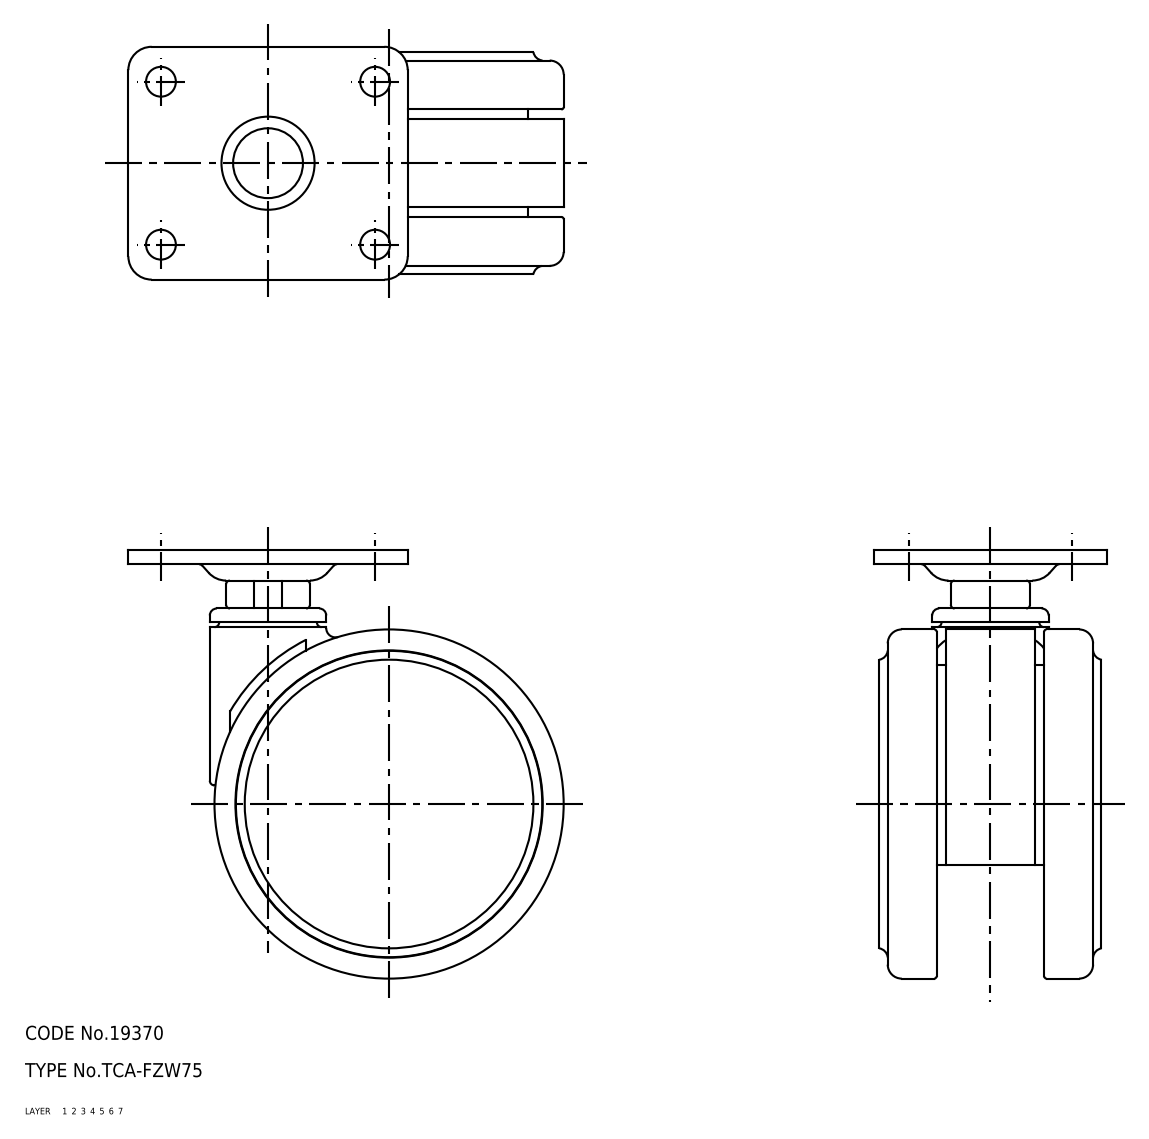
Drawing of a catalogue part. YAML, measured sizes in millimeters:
part_name: "caster; TCA-FZW75"
step_written_by: "SolidWorks 2015 (AUTOMOTIVE_DESIGN)"
units: millimeters
bodies: {solids: 2, faces: 1831, planar: 428, cylindrical: 783, other: 620}
overall_size: [93.5, 92, 50]
volume: 120349
surface_area: 74778
round_holes:
  - {diameter: 6.4, count: 4}
  - {diameter: 6.5, count: 1}
  - {diameter: 8, count: 1}
  - {diameter: 8.1, count: 1}
  - {diameter: 10.2, count: 1}
  - {diameter: 11, count: 1}
  - {diameter: 17, count: 1}
  - {diameter: 18.1, count: 1}
  - {diameter: 19, count: 1}
  - {diameter: 22.6, count: 1}
  - {diameter: 59, count: 1}
  - {diameter: 63, count: 1}
round_bosses_or_shafts:
  - {diameter: 16, count: 2}
  - {diameter: 14, count: 2}
  - {diameter: 65.8, count: 1}
  - {diameter: 54, count: 1}
  - {diameter: 26, count: 1}
  - {diameter: 25, count: 1}
  - {diameter: 10, count: 1}
  - {diameter: 8, count: 1}
partial_cylinders:
  - {radius: 1, count: 139}
  - {radius: 0.3, count: 132}
  - {radius: 0.5, count: 127}
  - {radius: 0.2, count: 16}
  - {radius: 2, count: 12}
  - {radius: 5, count: 4}
  - {radius: 6, count: 2}
  - {radius: 3, count: 1}
face_to_face_distances: [1.5, 46.2, 3.3, 1.8, 44.4, 42.9, 32.1, 9, 12.3, 35.4]
hole_center_spacings: [28.9, 35, 46, 57.8]
